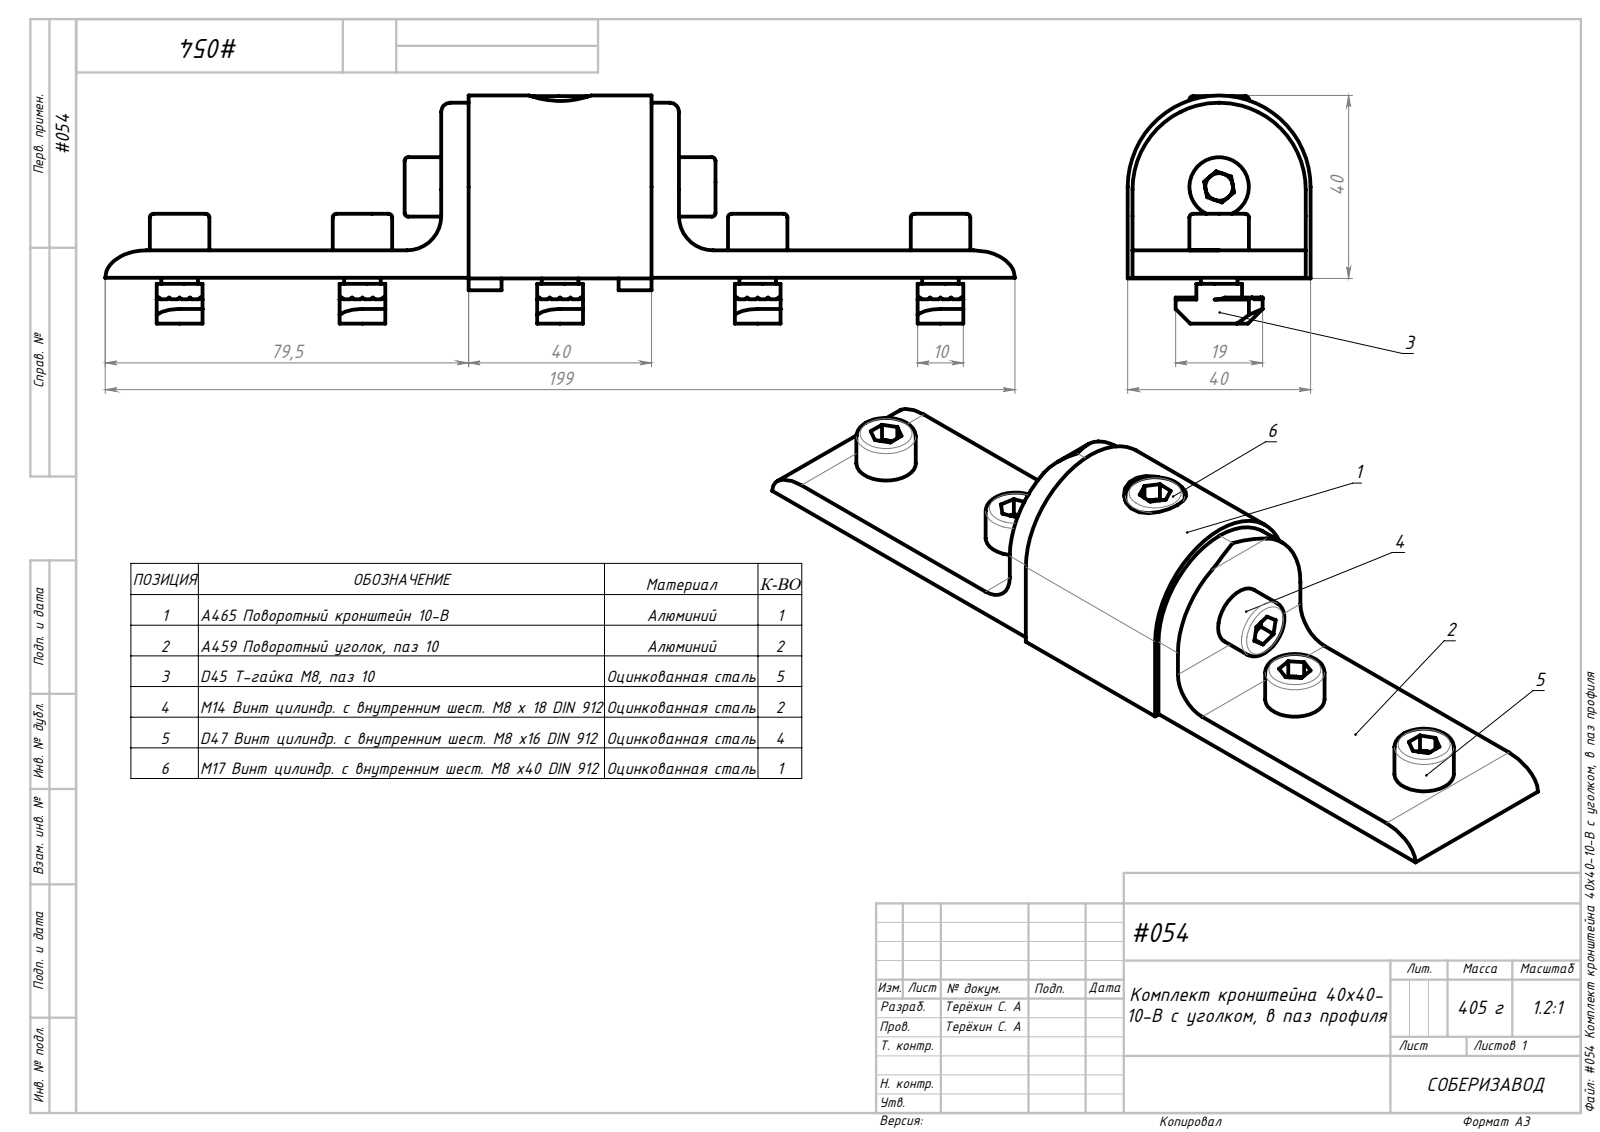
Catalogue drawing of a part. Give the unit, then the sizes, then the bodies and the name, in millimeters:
Units: millimetres
Overall size (bounding box): 199 × 49.88 × 40
Round holes (diameter × count): ⌀6.7 ×5, ⌀8.35 ×5, ⌀6.5 ×1, ⌀8.5 ×1, ⌀13.7 ×1
Round bosses / shafts (diameter × count): ⌀13 ×6, ⌀8 ×6
Partial cylindrical surfaces — rounded edges, fillets, slot ends (radius × count): R5.67 ×10, R6 ×10, R2 ×2, R7.5 ×2, R19 ×2, R20 ×1
Main face-to-face distances: 6, 40, 1.05, 38.95, 46, 6.13, 37.9, 10, 52, 16
Hole centre spacings: 40, 126.45, 39.99, 40.01, 43.22, 43.23, 83.22, 83.23
Volume: 118 061 mm³ · Surface area: 42 065 mm²
Bodies: 15 solids, 500 faces (321 planar, 87 cylindrical, 92 other)
Part name (STEP PRODUCT): A459 Поворотный уголок, паз 10; D47 Винт цилиндр. с внутренним шест. М8 х16 DIN 912; M17 Винт цилиндр. с внутренним шест. М8 х40 DIN 912; A465 Поворотный кронштейн 10-B (+3 more)
STEP written by: SolidWorks 2021 (AUTOMOTIVE_DESIGN)
